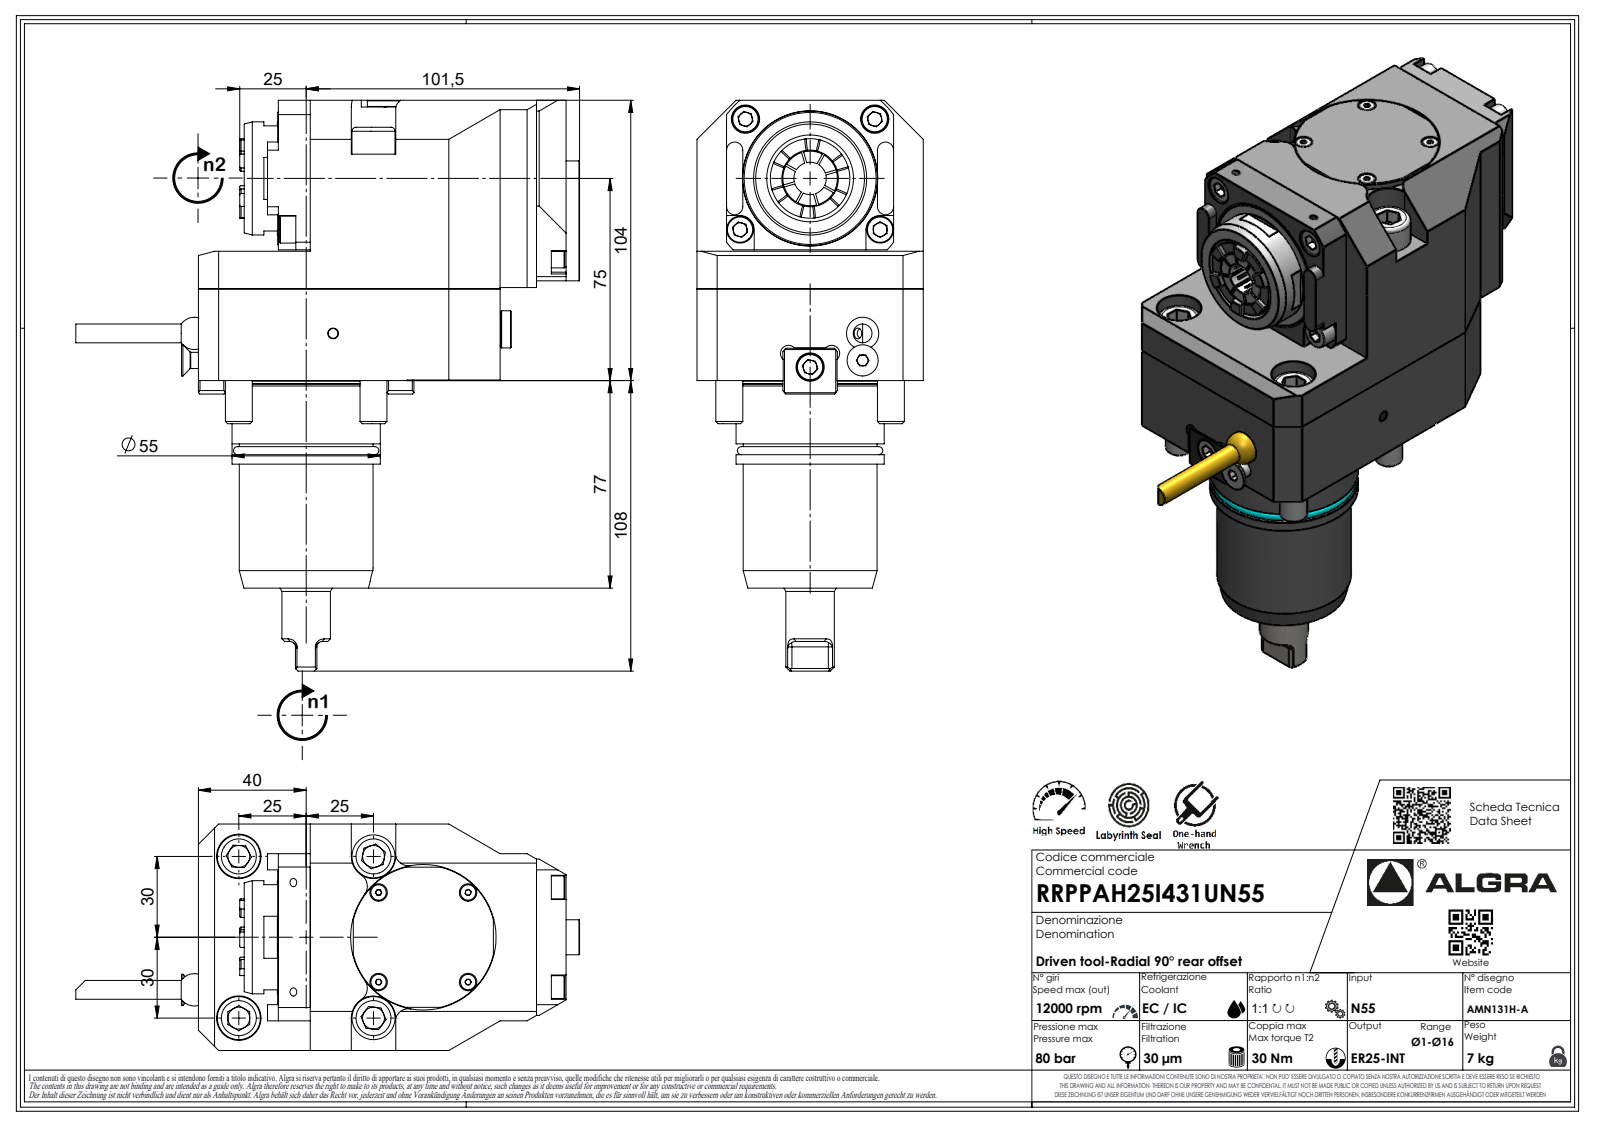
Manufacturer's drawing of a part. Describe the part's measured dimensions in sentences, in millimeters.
The part is named "RRPPAH25I431UN55". Its 3-D file was written by "SolidWorks 2023 (AUTOMOTIVE_DESIGN)". It is 2 solids with 569 faces: 382 planar, 84 cylindrical and 103 other. Overall it measures 211.8 by 187 by 84 millimeters. Its volume is 1 070 000 cubic millimeters and its surface area 83 111 square millimeters. Round holes: 2 of diameter 4, 1 of diameter 2.1, 1 of diameter 8.57, 1 of diameter 12. Round bosses or shafts: 4 of diameter 10, 2 of diameter 16, 1 of diameter 55, 1 of diameter 54.6, 1 of diameter 49.7, 1 of diameter 42, 1 of diameter 18, 1 of diameter 7. Partial cylindrical surfaces (rounded edges, fillets, slot ends): 7 of radius 0.33, 7 of radius 0.52, 7 of radius 2, 6 of radius 3, 4 of radius 3.7, 4 of radius 5, 3 of radius 8.25, 2 of radius 4. The main face-to-face distances are 84, 11, 24.5, 104, 56, 48, 112, 73, 47.8, 103.8.
